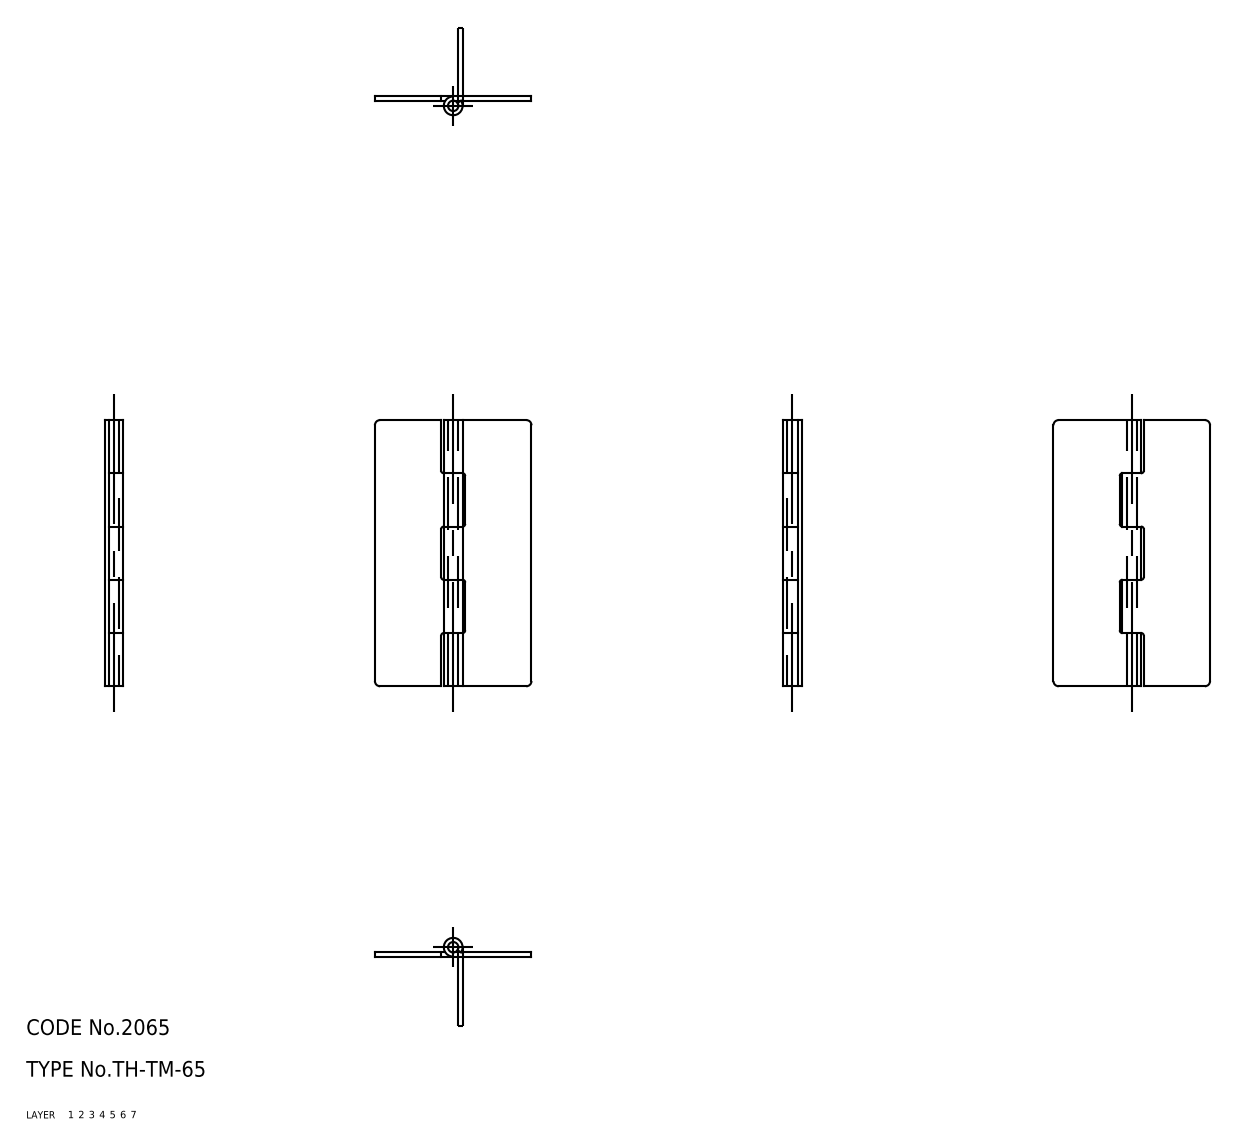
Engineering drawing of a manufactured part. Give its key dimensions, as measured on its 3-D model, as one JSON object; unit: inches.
{"part_name": "hinge piece_B; hinge piece_A; shaft; TH_TM_65_24782_36", "step_written_by": "CADfix (AUTOMOTIVE_DESIGN)", "units": "inches", "bodies": {"solids": 3, "faces": 54, "planar": 0, "cylindrical": 0, "other": 54}, "overall_size": [2.008, 1.181, 0.142], "volume_in3": 0.097, "surface_area_in2": 6.482}
